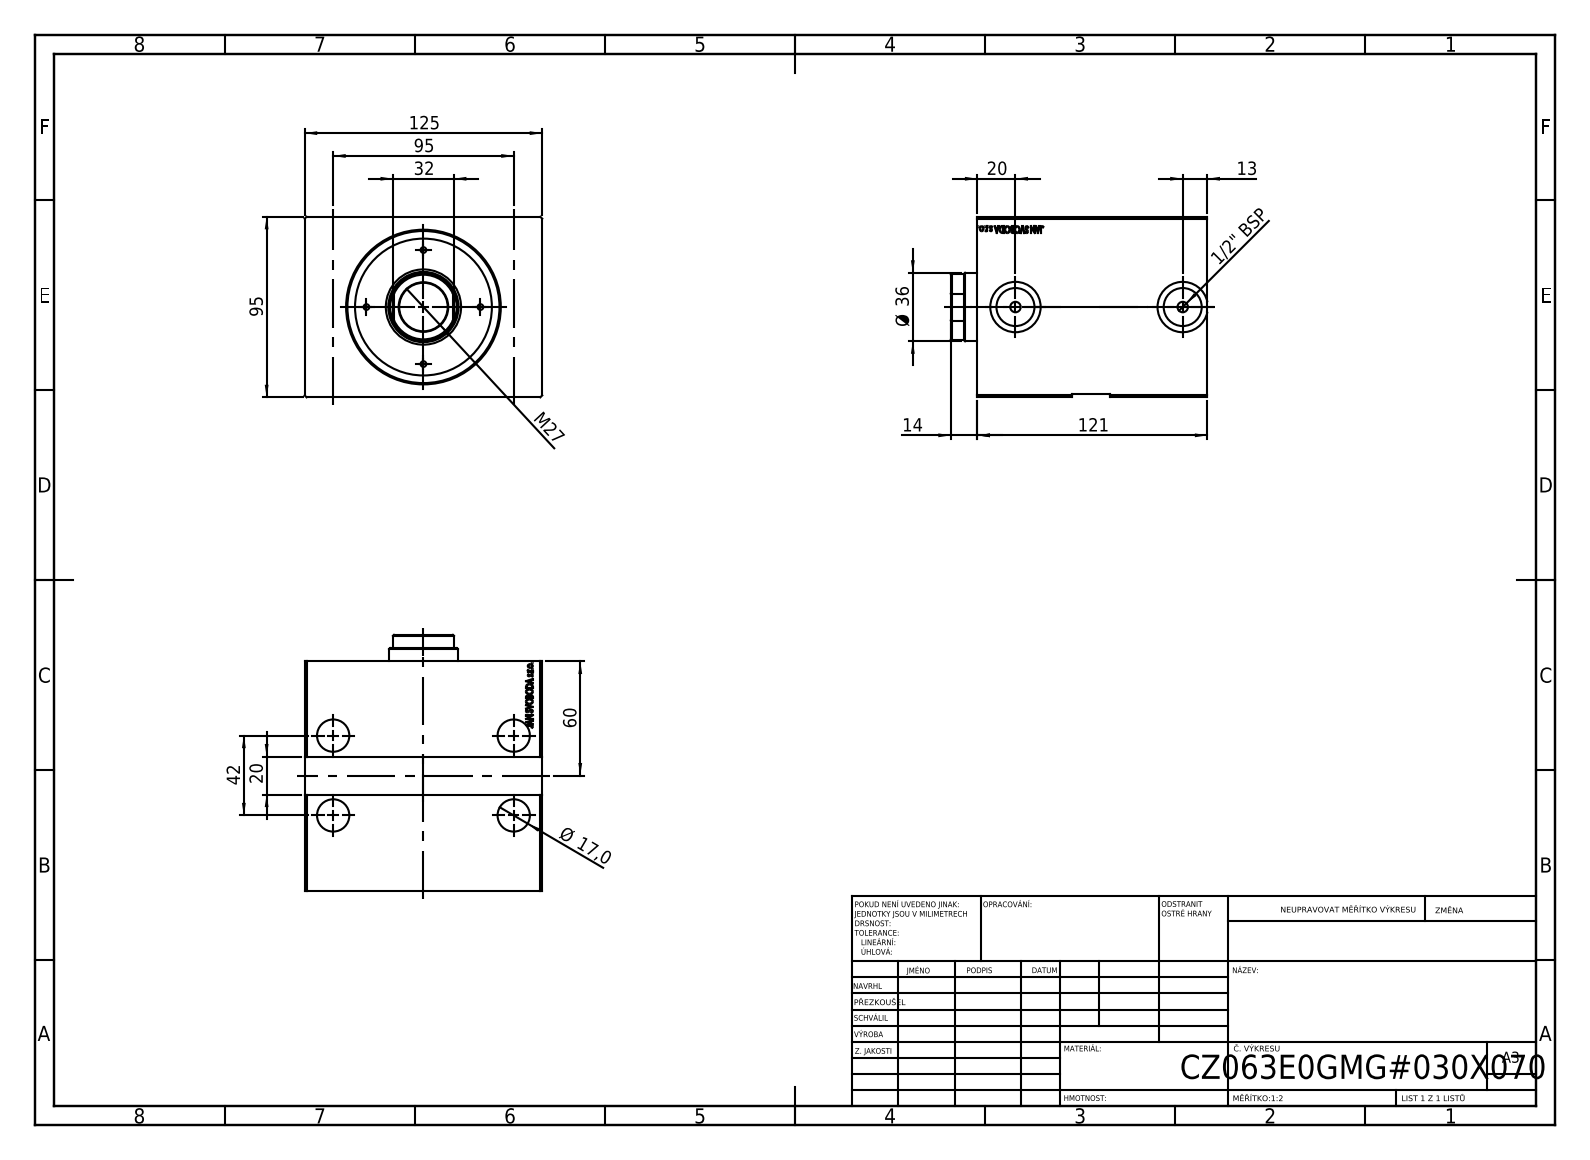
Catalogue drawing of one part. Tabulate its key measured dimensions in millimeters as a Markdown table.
| quantity | value |
| --- | --- |
| STEP written by | SolidWorks 2019 (CONFIG_CONTROL_DESIGN) |
| units | millimeters |
| bodies | 1 solid, 804 faces (393 planar, 29 cylindrical, 382 other) |
| overall size | 125 × 121 × 95 |
| volume | 997 308 mm³ |
| surface area | 118 243 mm² |
| round holes (diameter × count) | 17 × 4, 5.5 × 2, 8 × 2, 20 × 2, 26.5 × 2, 36 × 1, 63 × 1, 80 × 1 |
| main face-to-face distances | 95, 125, 121, 100.2, 20.8, 2, 93, 14, 86.2, 107 |
| hole center spacings | 42, 95, 103.87, 27.02, 28.79, 49.09, 51, 58.59 |
